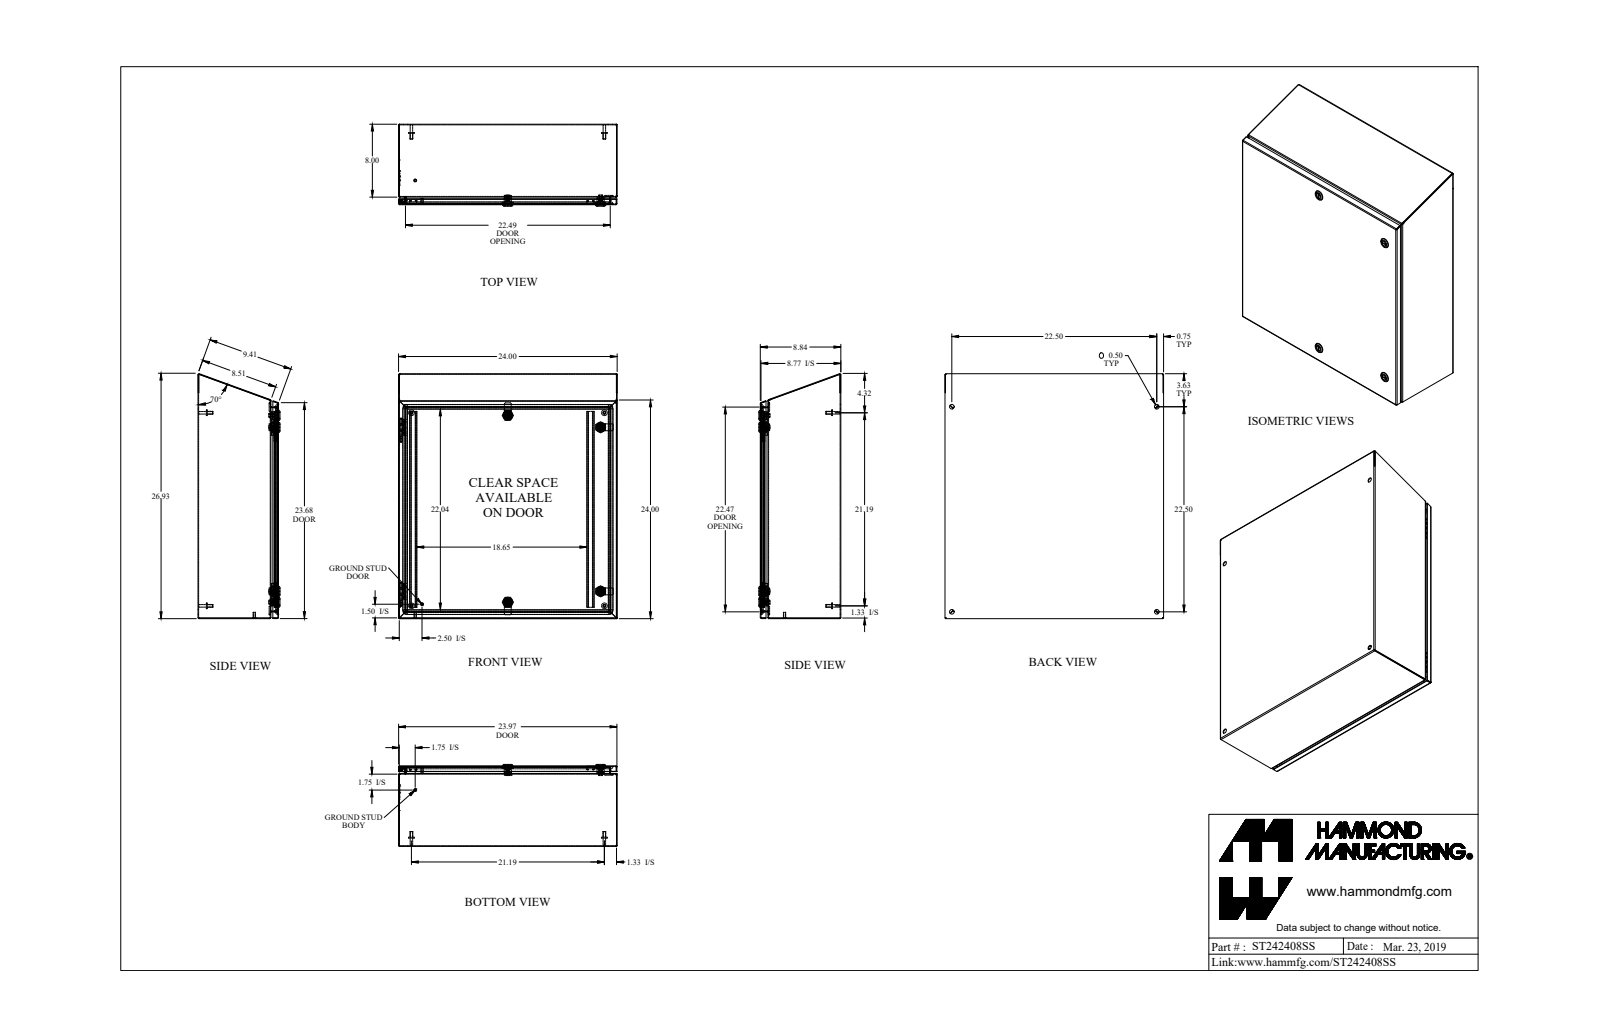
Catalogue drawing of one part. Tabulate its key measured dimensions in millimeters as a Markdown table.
| quantity | value |
| --- | --- |
| part name | ST242408SS |
| STEP written by | SolidWorks 2018 (AUTOMOTIVE_DESIGN) |
| units | millimeters |
| bodies | 39 solids, 1045 faces (596 planar, 309 cylindrical, 140 other) |
| overall size | 682.8 × 609.6 × 228.5 |
| volume | 2 828 000 mm³ |
| surface area | 3 112 000 mm² |
| round holes (diameter × count) | 12.7 × 8, 5 × 4, 9.8 × 4, 16 × 4, 19.5 × 4, 4.4 × 1, 6.1 × 1, 6.1 × 1 |
| round bosses / shafts (diameter × count) | 15.9 × 8, 8 × 6, 27.9 × 4, 13.3 × 4, 7 × 4, 6 × 4, 19.9 × 3, 6.4 × 2 |
| partial cylindrical surfaces (radius × count) | 0.9 × 20, 2.7 × 20, 0.3 × 12, 1.2 × 12, 6.4 × 11, 3.2 × 8, 0.2 × 4, 1.6 × 4 |
| main face-to-face distances | 1.8, 222.6, 220.8, 224.5, 607.8, 605.9, 609.6, 201.4, 21.3, 203.2 |
| hole center spacings | 571.5, 63.3, 515.1, 547.2, 748.8, 808.2, 260.6, 260.9 |
